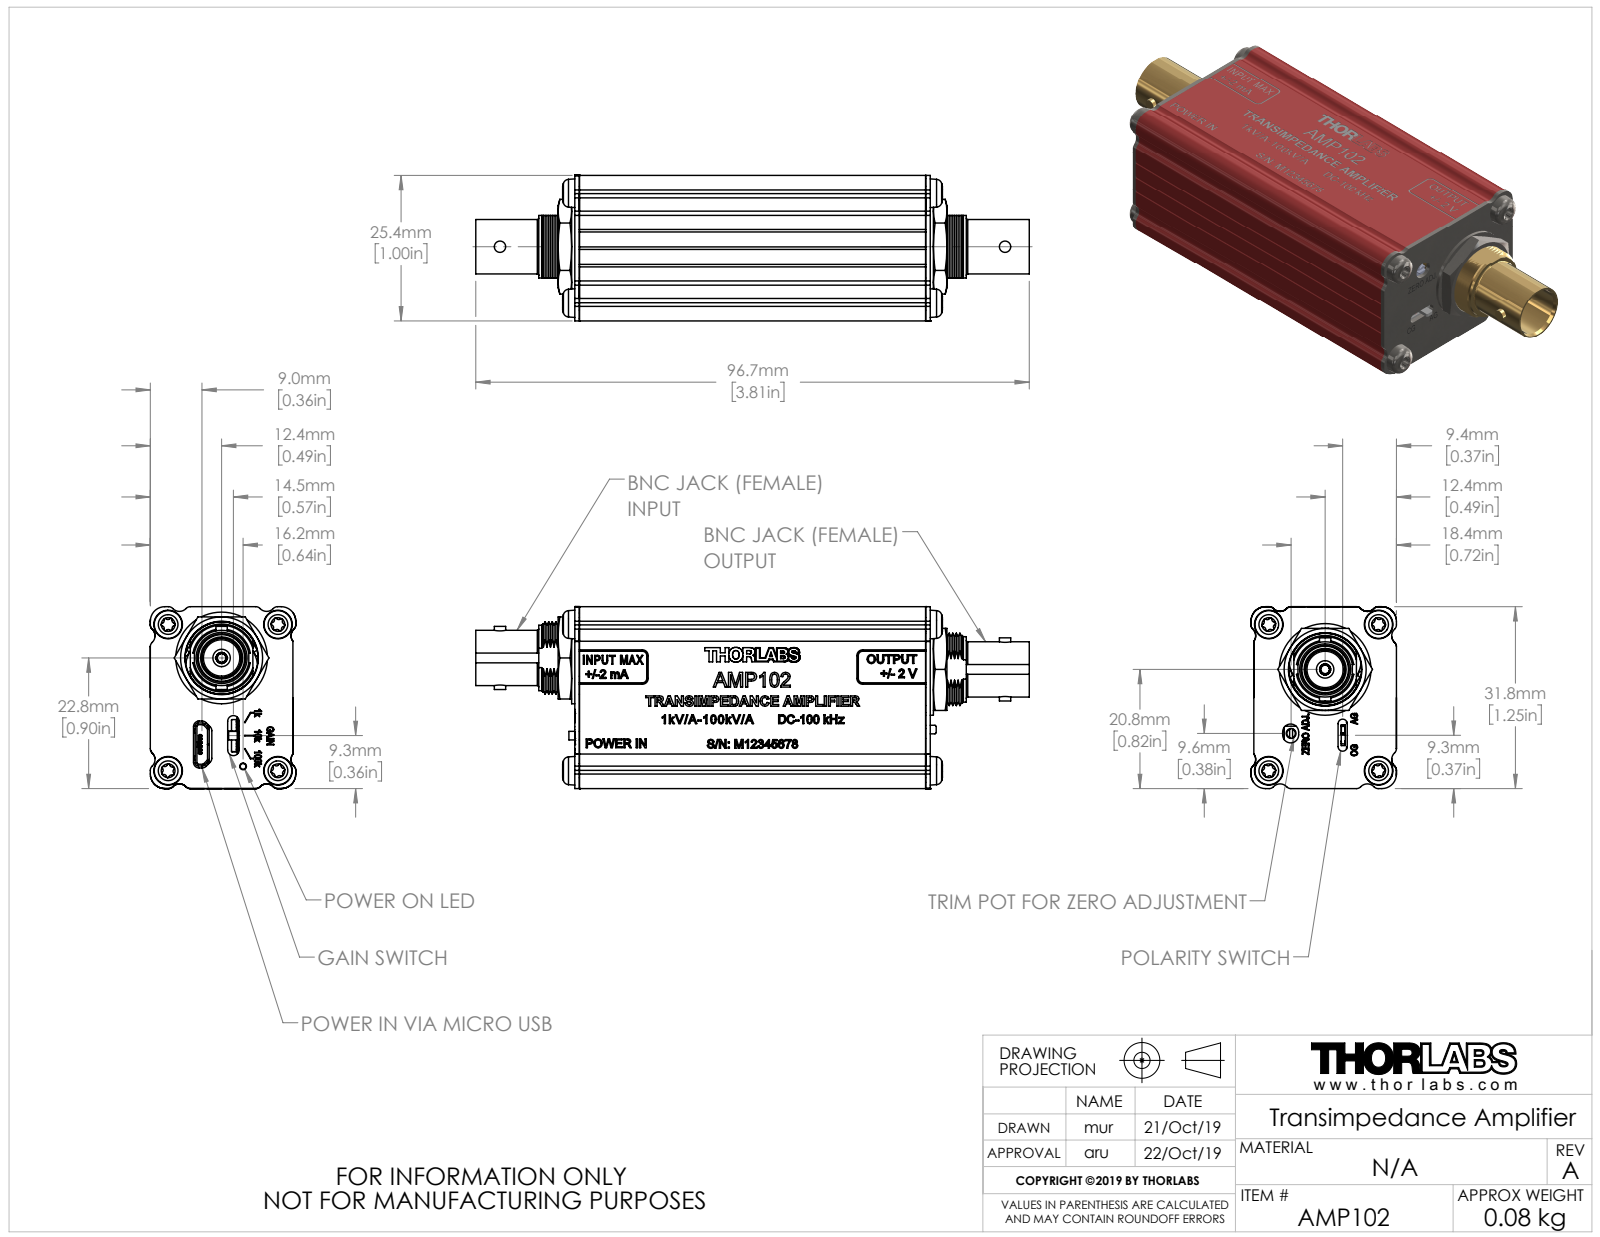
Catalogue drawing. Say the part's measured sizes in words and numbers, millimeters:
The part is named "19.12.06_AMP102 WEB". Its 3-D file was written by "SolidWorks 2018 (AUTOMOTIVE_DESIGN)". It is 0 solids with 4731 faces: 3144 planar, 665 cylindrical and 922 other. Overall it measures 96.65 by 31.75 by 25.4 millimeters. Round holes: 8 of diameter 3.5, 4 of diameter 0.2, 4 of diameter 0.6, 2 of diameter 0.85, 2 of diameter 0.9, 2 of diameter 1.19, 2 of diameter 1.49, 2 of diameter 1.93, 2 of diameter 4.04, 2 of diameter 6.93, 2 of diameter 8.86, 2 of diameter 12.7. Round bosses or shafts: 6 of diameter 0.46, 4 of diameter 2.5, 4 of diameter 2.22, 2 of diameter 16, 2 of diameter 11.43, 2 of diameter 10.46, 2 of diameter 9.65, 2 of diameter 6.91. Partial cylindrical surfaces (rounded edges, fillets, slot ends): 48 of radius 0.24, 48 of radius 0.42, 40 of radius 0.2, 37 of radius 0.1, 23 of radius 0.15, 22 of radius 1.02, 14 of radius 0.25, 12 of radius 0.4. The main face-to-face distances are 1.27, 3.05, 1.64, 0.8, 9.14, 6.1, 12.19, 17.91, 61.28, 4.32. The hole center spacings are 2, 19.18, 1.11, 14.86, 25.53, 31.93, 5, 11.08.
